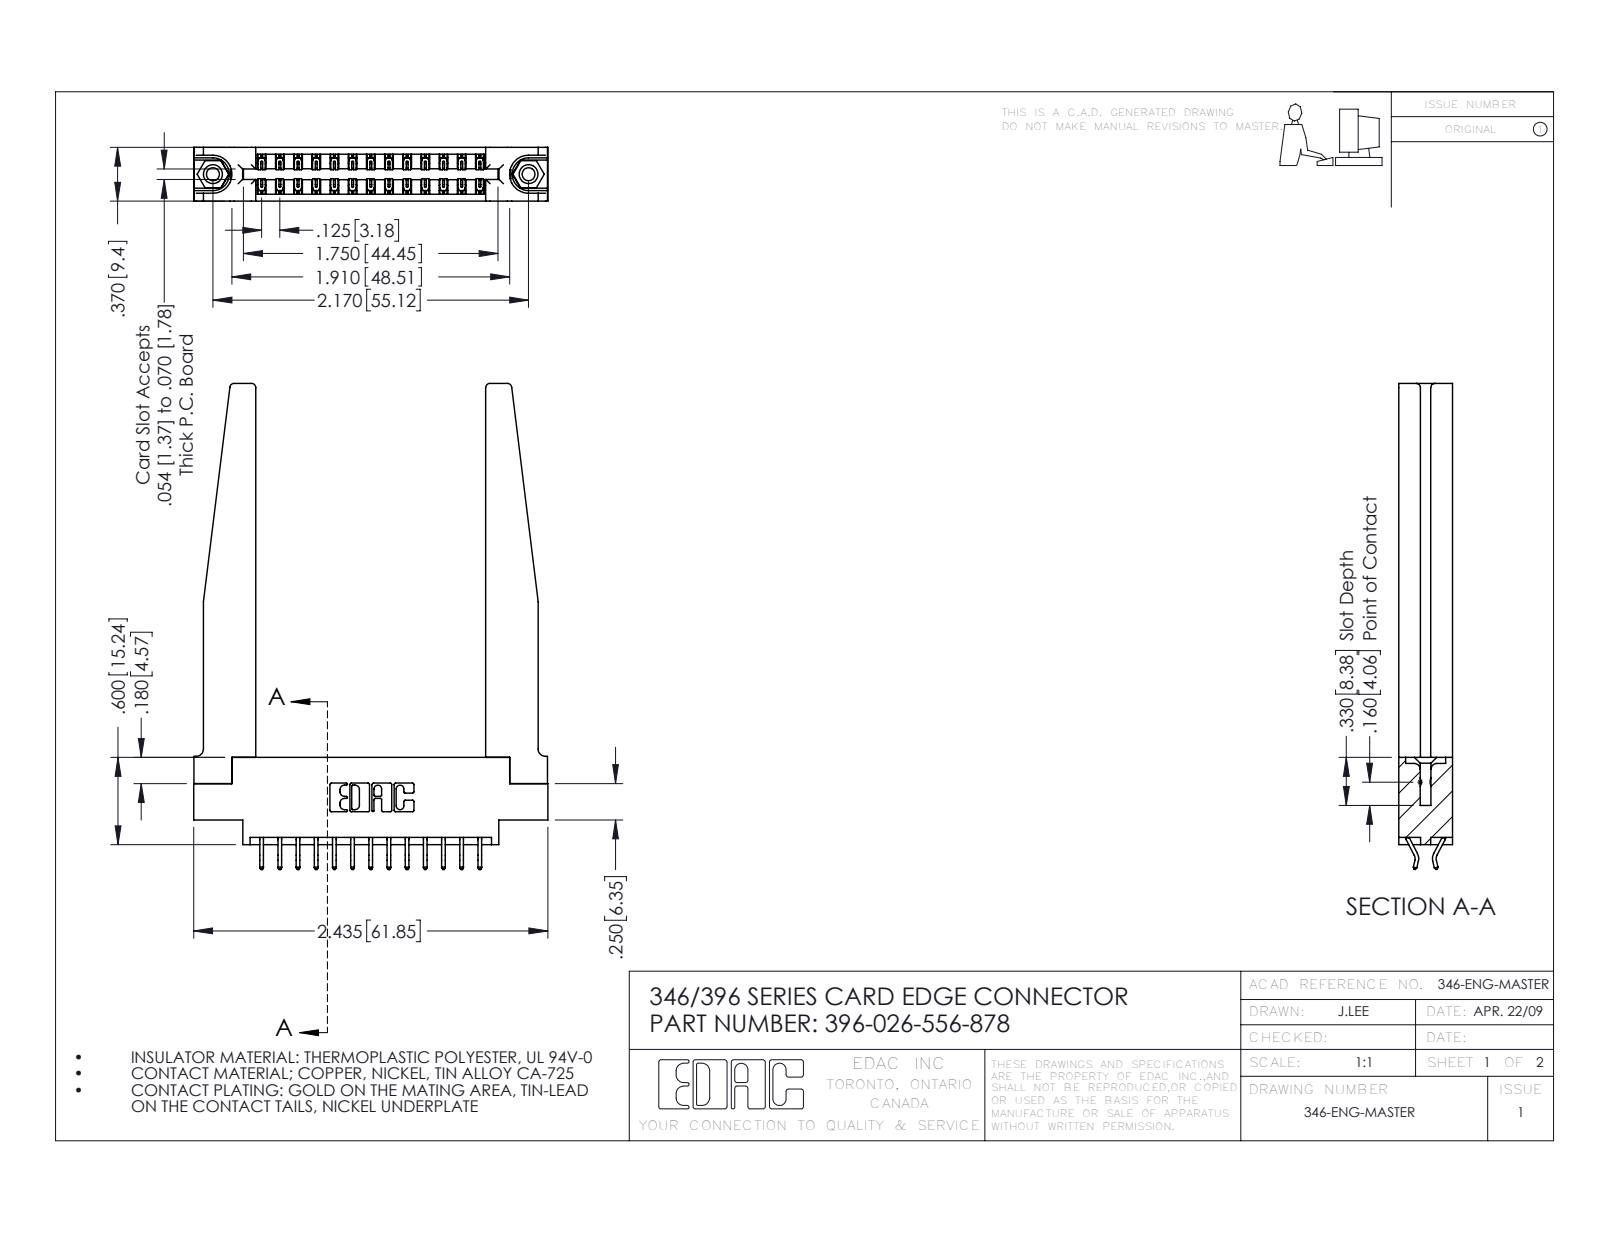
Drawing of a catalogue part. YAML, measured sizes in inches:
part_name: "346 Part_0.170 Offset - 0.156 Dia-TH; 345-250-001_345-250-001-102; 346-220-078_345-220-078; 345-292-001_556 Tail (+1 more)"
step_written_by: "SolidWorks 2016 (CONFIG_CONTROL_DESIGN)"
units: inches
bodies: {solids: 31, faces: 1868, planar: 1236, cylindrical: 580, other: 52}
overall_size: [3.34, 2.435, 0.37]
volume: 0.766
surface_area: 21.71
round_holes:
  - {diameter: 0.089, count: 2}
  - {diameter: 0.125, count: 2}
  - {diameter: 0.156, count: 2}
  - {diameter: 0.064, count: 1}
round_bosses_or_shafts:
  - {diameter: 0.155, count: 2}
partial_cylinders:
  - {radius: 0.006, count: 39}
  - {radius: 0.01, count: 22}
  - {radius: 0.03, count: 8}
  - {radius: 0.007, count: 6}
  - {radius: 0.031, count: 6}
  - {radius: 0.05, count: 4}
  - {radius: 0.026, count: 3}
  - {radius: 0.01, count: 2}
face_to_face_distances: [0.37, 0.15, 0.072, 0.148, 0.048, 0.322, 0.25, 0.102, 0.22, 0.173]
hole_center_spacings: [0.246, 1.964, 2.17]
